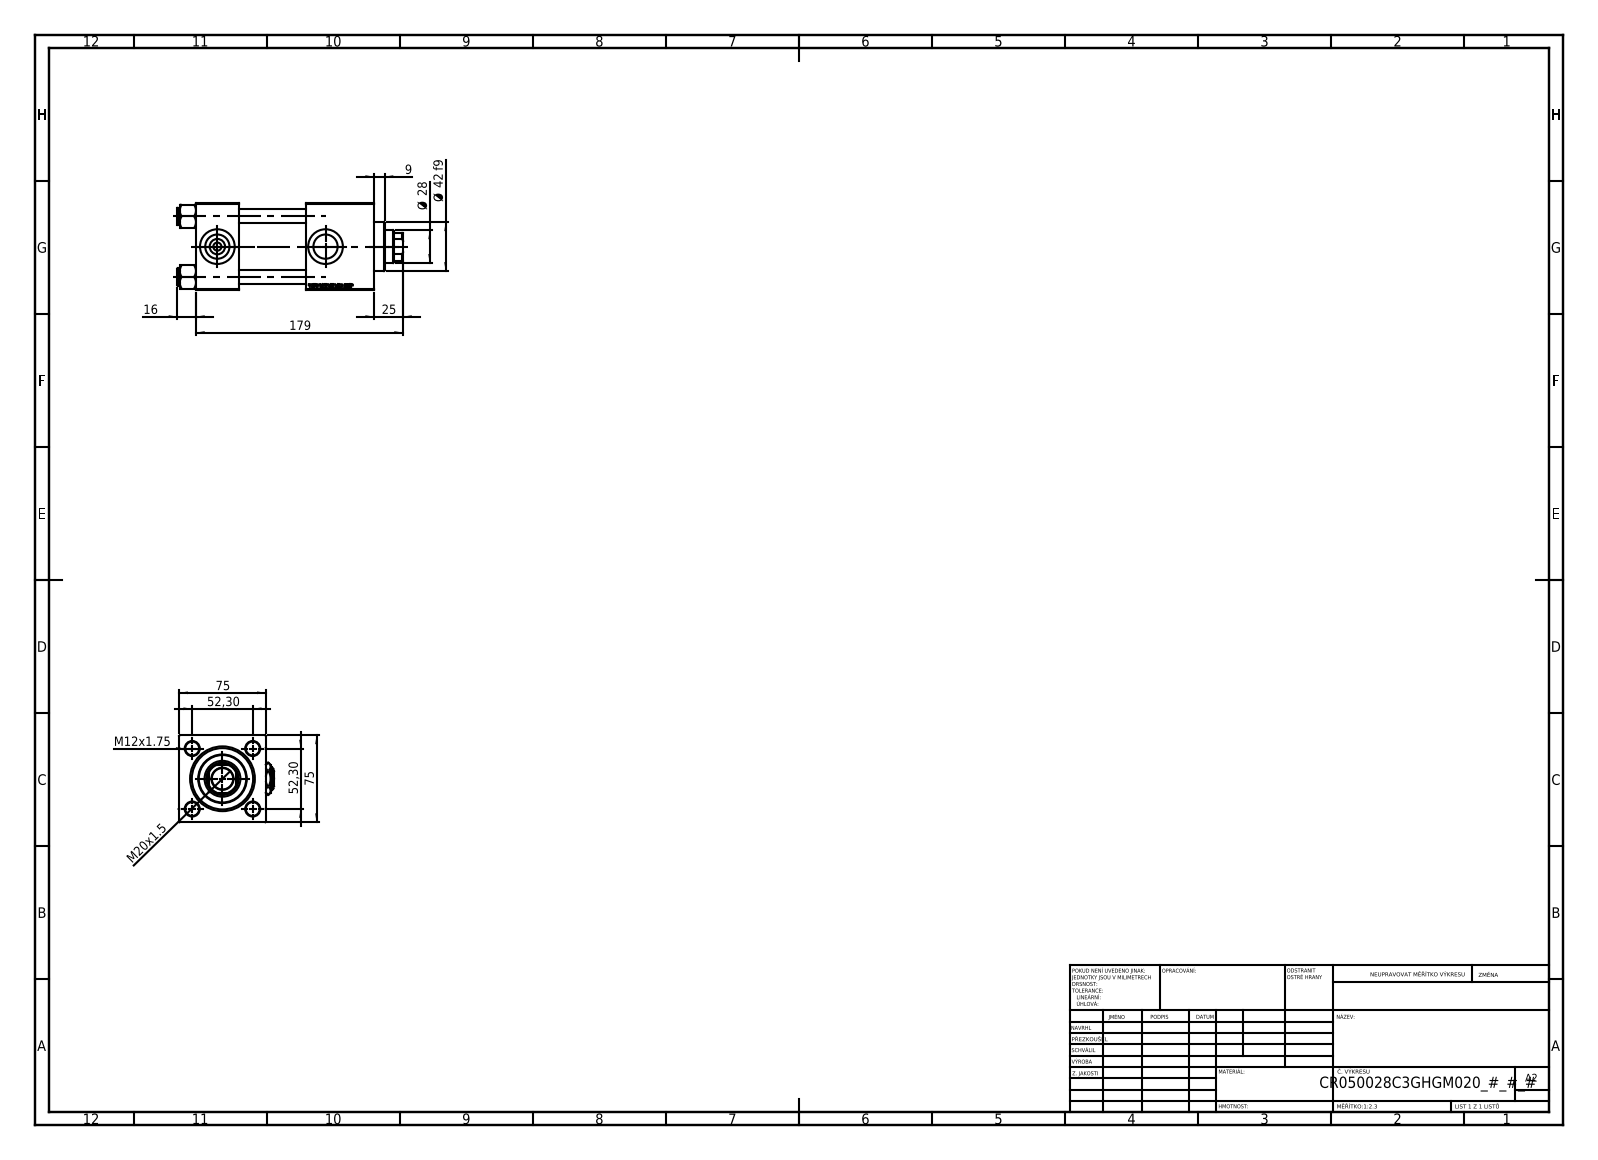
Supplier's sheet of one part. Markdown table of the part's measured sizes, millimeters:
| quantity | value |
| --- | --- |
| part name | V215CR_VCP_C; NUT_M5_C; V215_VC_A; Zatka_pro_OIL_PORT (+2 more) |
| STEP written by | SolidWorks 2019 (CONFIG_CONTROL_DESIGN) |
| units | millimeters |
| bodies | 13 solids, 1249 faces (573 planar, 98 cylindrical, 578 other) |
| overall size | 195 × 82.27 × 75 |
| volume | 663 959 mm³ |
| surface area | 155 409 mm² |
| round holes (diameter × count) | 12 × 4, 7 × 2, 20.96 × 2, 30 × 2, 18.5 × 1, 28 × 1, 31 × 1, 41 × 1, 50 × 1, 53 × 1 |
| round bosses / shafts (diameter × count) | 15 × 4, 56 × 1, 42 × 1 |
| partial cylindrical surfaces (radius × count) | 13.5 × 1 |
| main face-to-face distances | 75, 37, 154, 117, 95, 58, 59, 125.3, 88.3, 30.3 |
| hole center spacings | 36.98, 52.3, 73.96, 93.5 |
